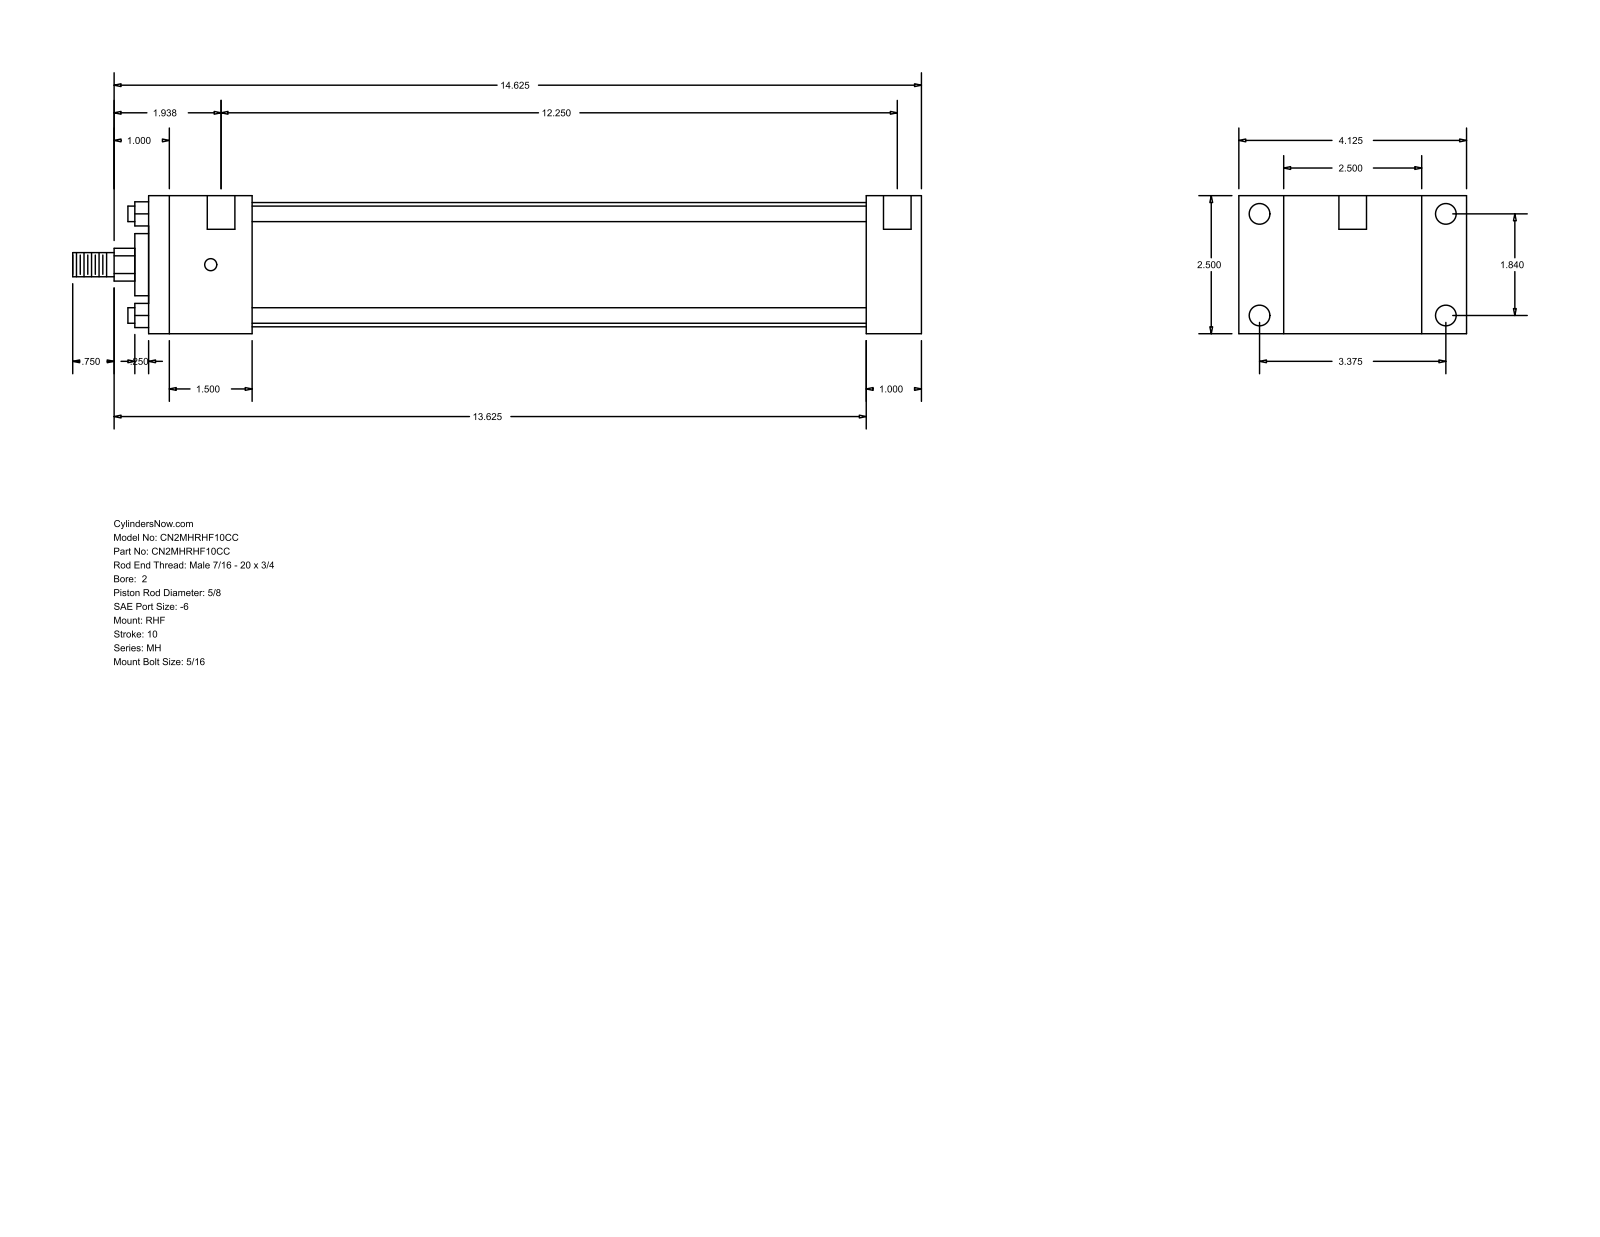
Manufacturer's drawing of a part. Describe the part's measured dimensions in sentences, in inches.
The part is named "MH_RHF__0200_0.625". Its 3-D file was written by "GSSL Pune (CONFIG_CONTROL_DESIGN)". It is 0 solids with 88 faces: 60 planar, 28 cylindrical and 0 other. Overall it measures 15.375 by 4.125 by 2.5 inches. Round holes: 4 of diameter 0.219, 4 of diameter 0.375, 2 of diameter 0.5. Round bosses or shafts: 4 of diameter 0.281, 1 of diameter 2.25, 1 of diameter 1.125, 1 of diameter 0.625, 1 of diameter 0.437. Partial cylindrical surfaces (rounded edges, fillets, slot ends): 1 of radius 0.297. The main face-to-face distances are 2.5, 1, 0.813, 3.313, 13, 14, 4.125, 1.875, 11.125, 12.125. The hole center spacings are 1.84, 3.375, 3.844, 12.563, 0.125, 0.187, 12.25, 12.375.
